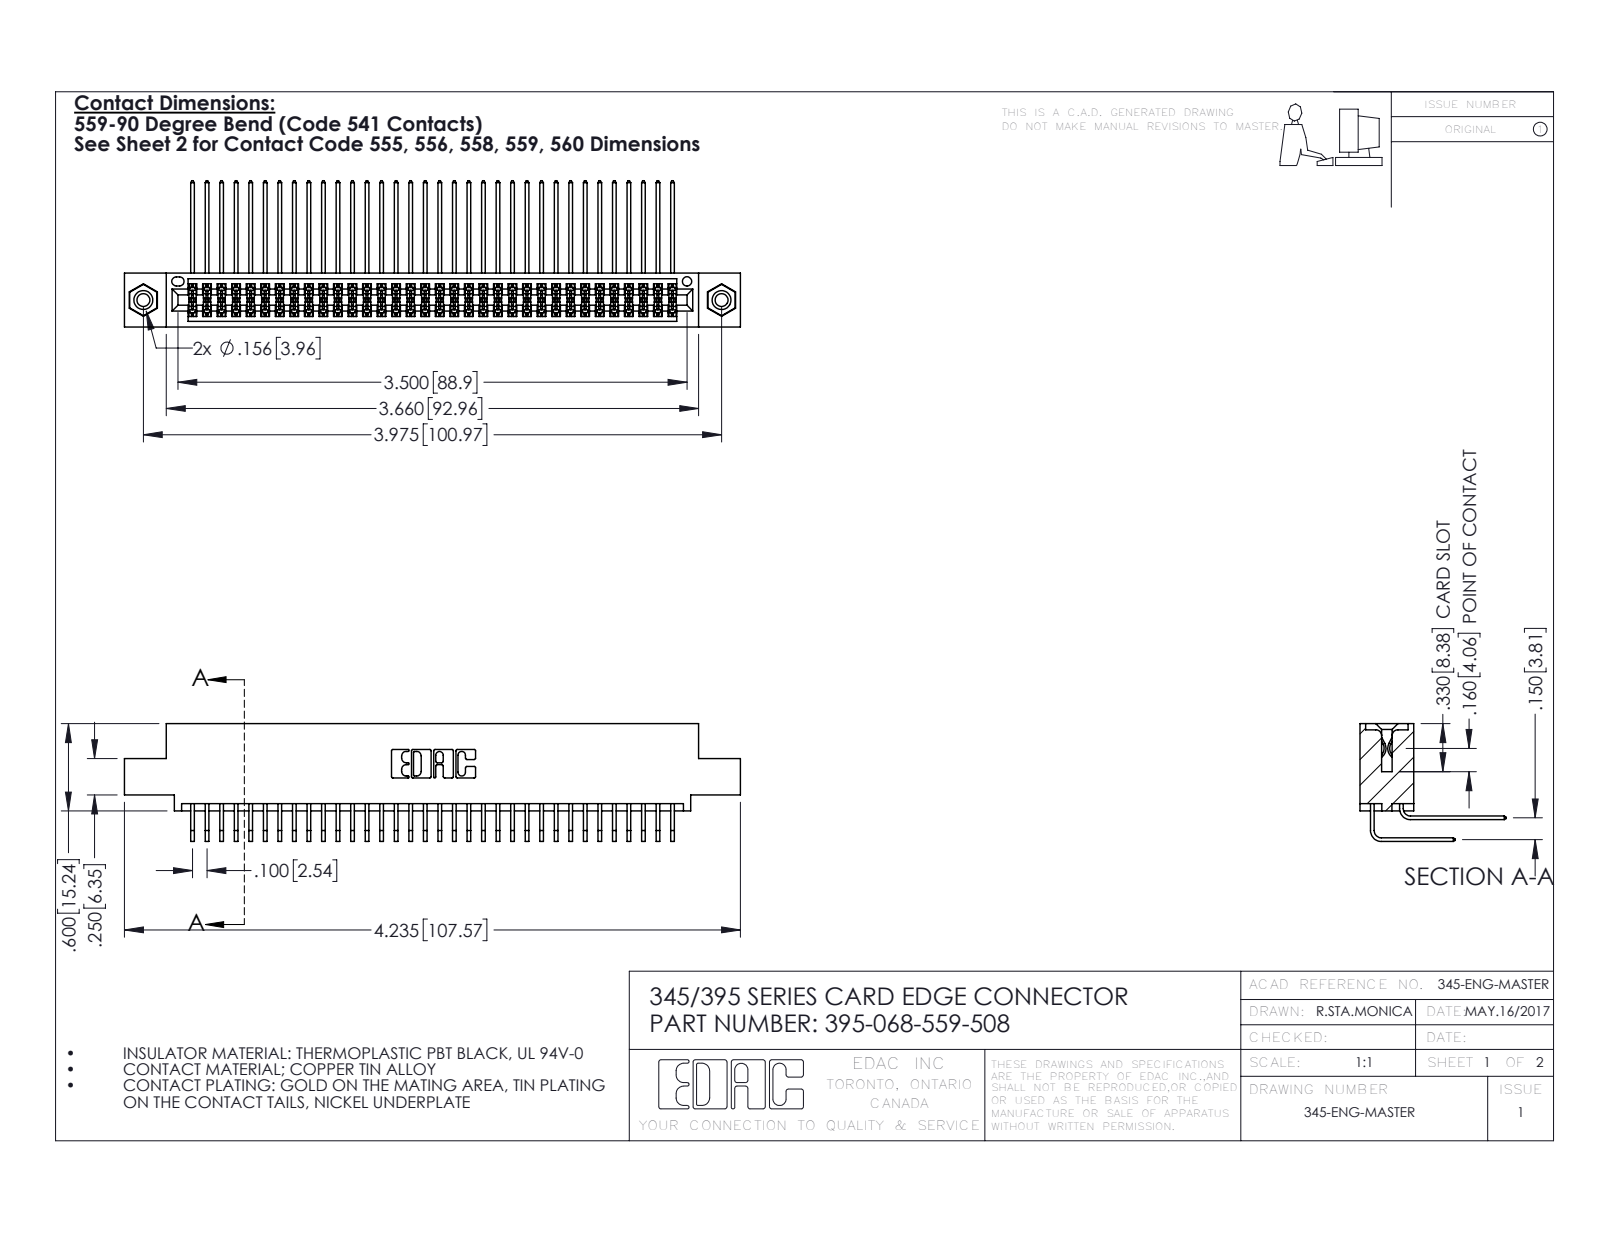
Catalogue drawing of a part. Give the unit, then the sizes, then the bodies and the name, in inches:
Units: inches
Overall size (bounding box): 4.235 × 1.005 × 0.809
Round holes (diameter × count): ⌀0.089 ×2, ⌀0.125 ×2, ⌀0.156 ×2, ⌀0.064 ×1
Round bosses / shafts (diameter × count): ⌀0.155 ×2
Partial cylindrical surfaces — rounded edges, fillets, slot ends (radius × count): R0.006 ×103, R0.01 ×22, R0.007 ×6, R0.031 ×6, R0.026 ×3, R0.014 ×2, R0.019 ×2, R0.022 ×2
Main face-to-face distances: 0.072, 0.298, 0.2, 0.37, 0.098, 0.272, 0.025, 0.225, 0.175, 0.15
Hole centre spacings: 0.27, 3.74, 3.975
Volume: 0.652 in³ · Surface area: 27.27 in²
Bodies: 71 solids, 3726 faces (2496 planar, 1214 cylindrical, 16 other)
Part name (STEP PRODUCT): 345 Part_0.110 Offset - 0.156 Dia-TI; 345-250-001_345-250-003-102; 395-068-559-508; 345-292-001_558 559 Tail - 1 (+1 more)
STEP written by: SolidWorks 2016 (CONFIG_CONTROL_DESIGN)
